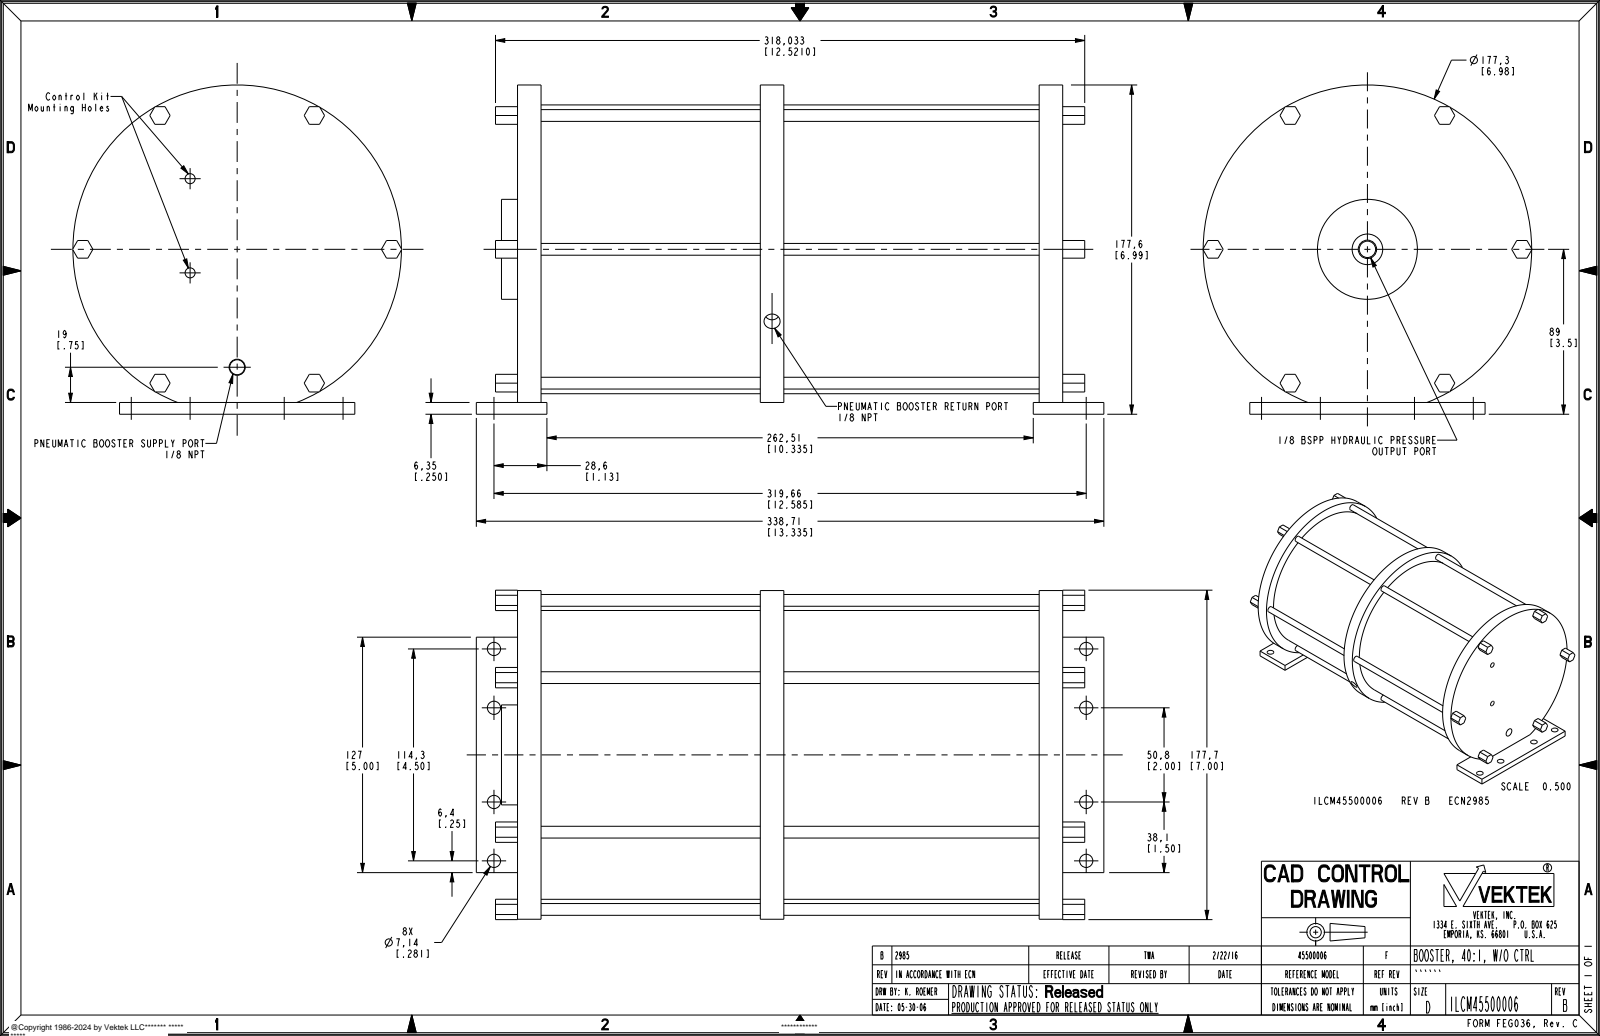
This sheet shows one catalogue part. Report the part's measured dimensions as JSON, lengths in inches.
{"part_name": "ILCM45500006", "step_written_by": "PRO/ENGINEER BY PARAMETRIC TECHNOLOGY CORPORATION, 2013320 (CONFIG_CONTROL_DESIGN)", "units": "inches", "bodies": {"solids": 1, "faces": 243, "planar": 128, "cylindrical": 87, "other": 28}, "overall_size": [13.335, 6.996, 6.992], "volume_in3": 362.8, "surface_area_in2": 431.6, "round_holes": [[0.281, 12], [0.25, 6], [0.201, 4], [0.213, 2], [0.348, 1], [0.65, 1]], "round_bosses_or_shafts": [[0.25, 6], [6.98, 1], [6.133, 1], [2.123, 1], [0.383, 1]], "face_to_face_distances": [11.585, 0.5, 11.085, 5.159, 5.926, 0.25, 5.659, 4.659, 10.585, 6.426], "hole_center_spacings": [0.75, 1.25, 1.458, 2, 2.136, 3.25, 3.335, 11.835]}
